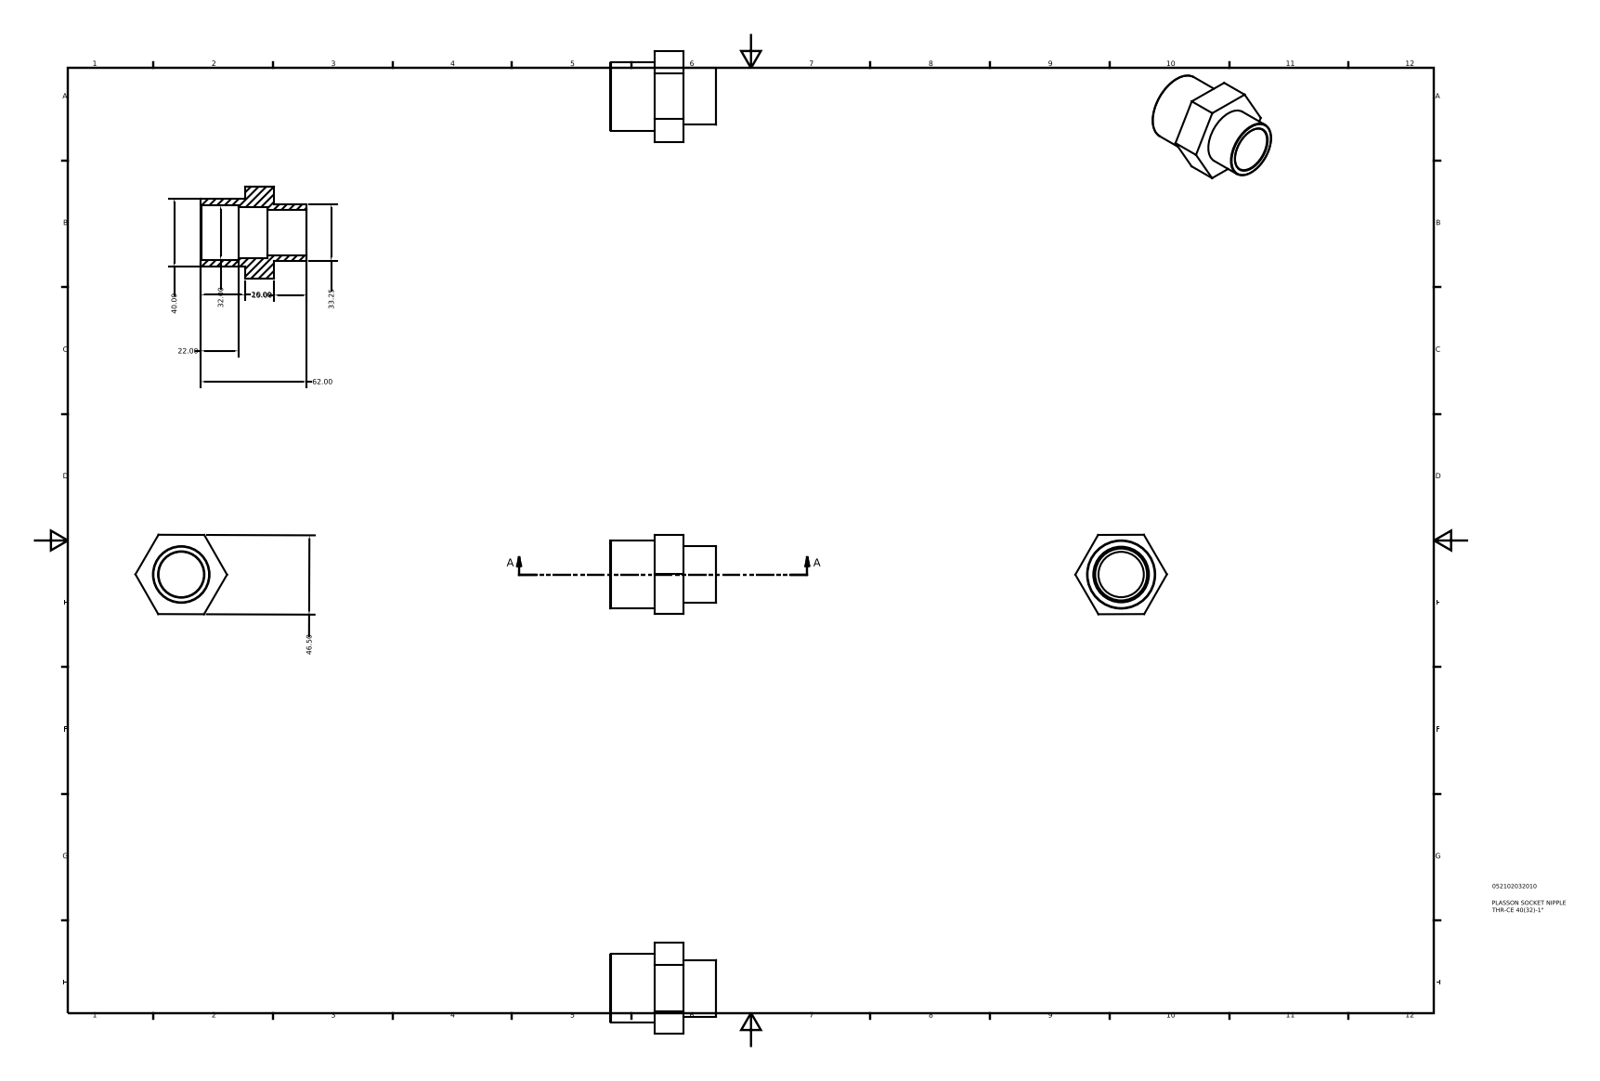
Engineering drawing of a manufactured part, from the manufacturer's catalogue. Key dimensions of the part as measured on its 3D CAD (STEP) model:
Part name (STEP PRODUCT): 052102032010
STEP written by: Autodesk Inventor 2015 (AUTOMOTIVE_DESIGN)
Units: millimetres
Bodies: 1 solid, 21 faces (12 planar, 5 cylindrical, 4 other)
Overall size (bounding box): 62 × 53.69 × 46.6
Volume: 38 147 mm³ · Surface area: 16 327 mm²
Round holes (diameter × count): ⌀26.6 ×1, ⌀30.4 ×1, ⌀32 ×1
Round bosses / shafts (diameter × count): ⌀40 ×1, ⌀33.25 ×1
Main face-to-face distances: 17, 46.51, 46.48, 46.5, 26, 43, 62, 36, 19, 39.2
